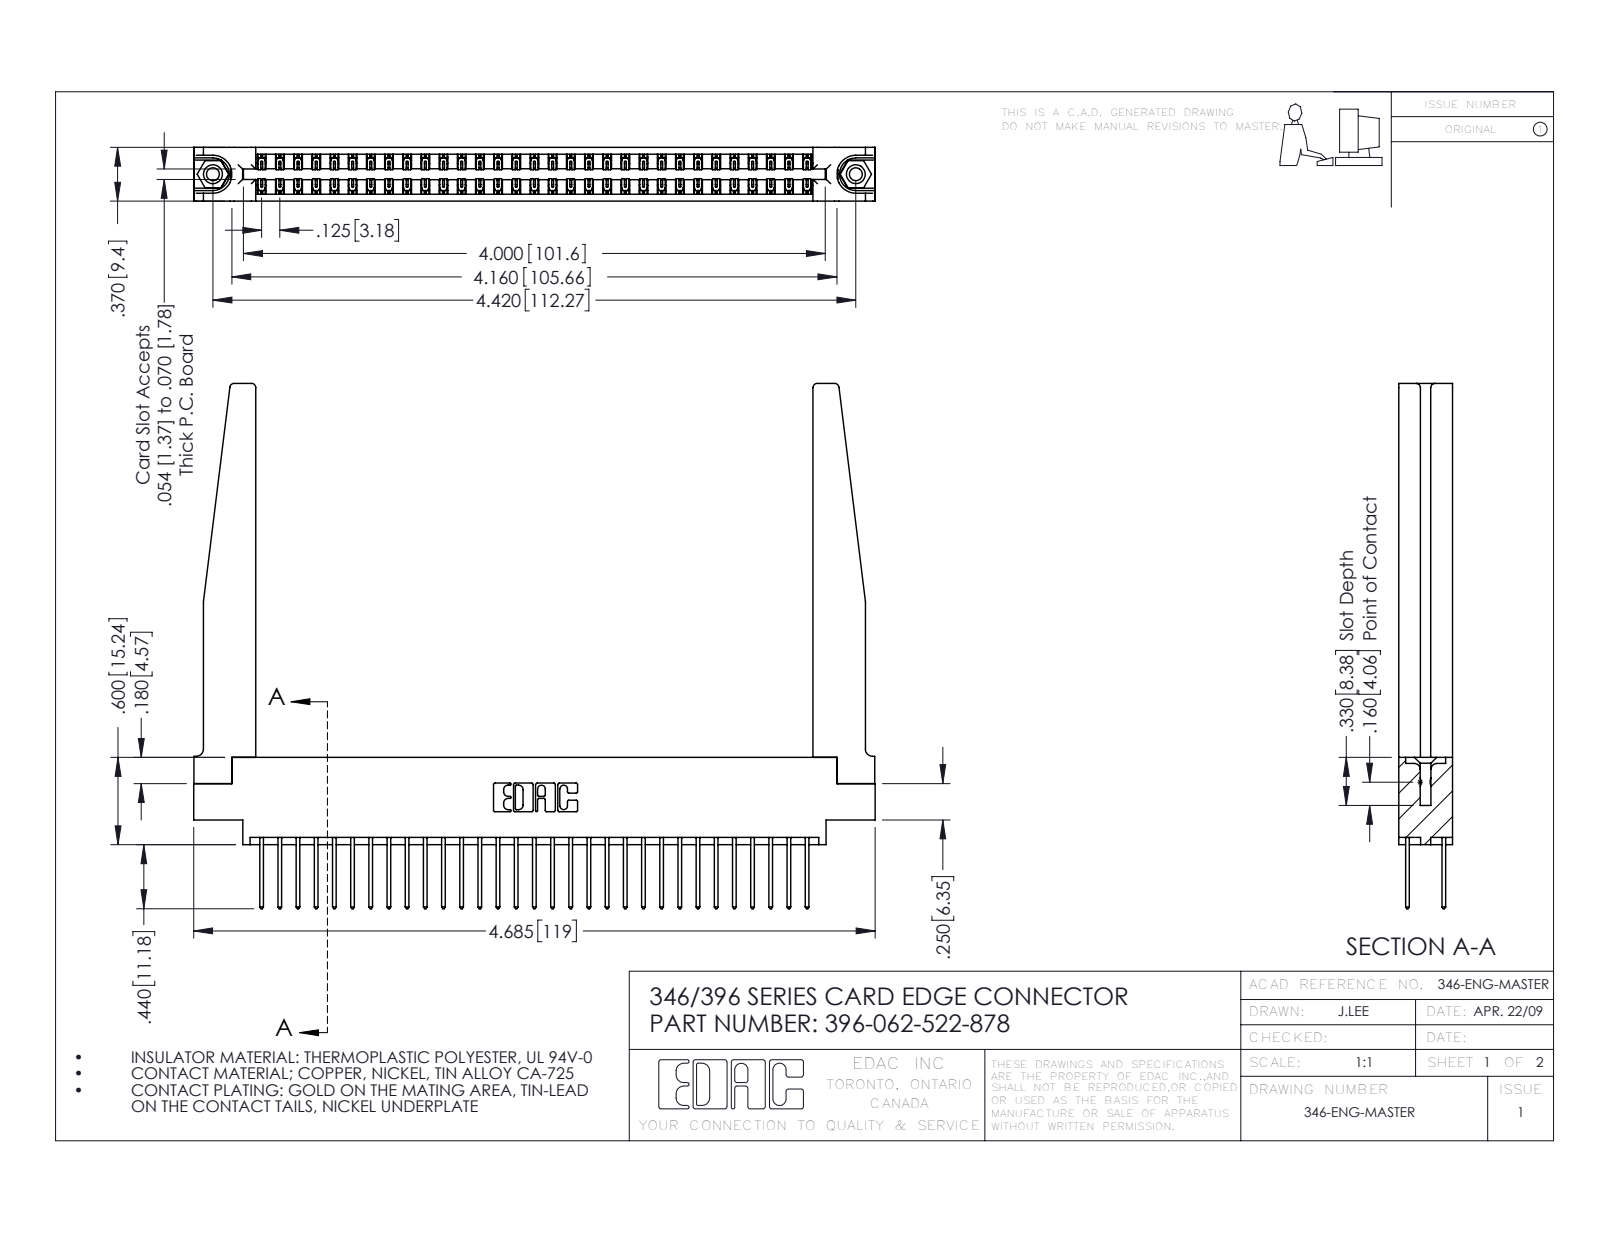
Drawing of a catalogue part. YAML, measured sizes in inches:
part_name: "345-292-001_345-293-122; 396-062-522-878; 346 Part_0.170 Offset - 0.156 Dia-TH; 346-220-078_345-220-078 (+1 more)"
step_written_by: "SolidWorks 2016 (CONFIG_CONTROL_DESIGN)"
units: inches
bodies: {solids: 67, faces: 3584, planar: 2392, cylindrical: 1140, other: 52}
overall_size: [4.685, 3.61, 0.37]
volume: 1.125
surface_area: 35.84
round_holes:
  - {diameter: 0.089, count: 2}
  - {diameter: 0.125, count: 2}
  - {diameter: 0.156, count: 2}
  - {diameter: 0.064, count: 1}
round_bosses_or_shafts:
  - {diameter: 0.155, count: 2}
partial_cylinders:
  - {radius: 0.006, count: 93}
  - {radius: 0.01, count: 62}
  - {radius: 0.01, count: 22}
  - {radius: 0.03, count: 8}
  - {radius: 0.007, count: 6}
  - {radius: 0.031, count: 6}
  - {radius: 0.026, count: 3}
  - {radius: 0.014, count: 2}
face_to_face_distances: [0.37, 0.048, 0.322, 0.072, 0.25, 0.298, 0.025, 0.148, 0.15, 0.275]
hole_center_spacings: [0.246, 4.212, 4.42]
